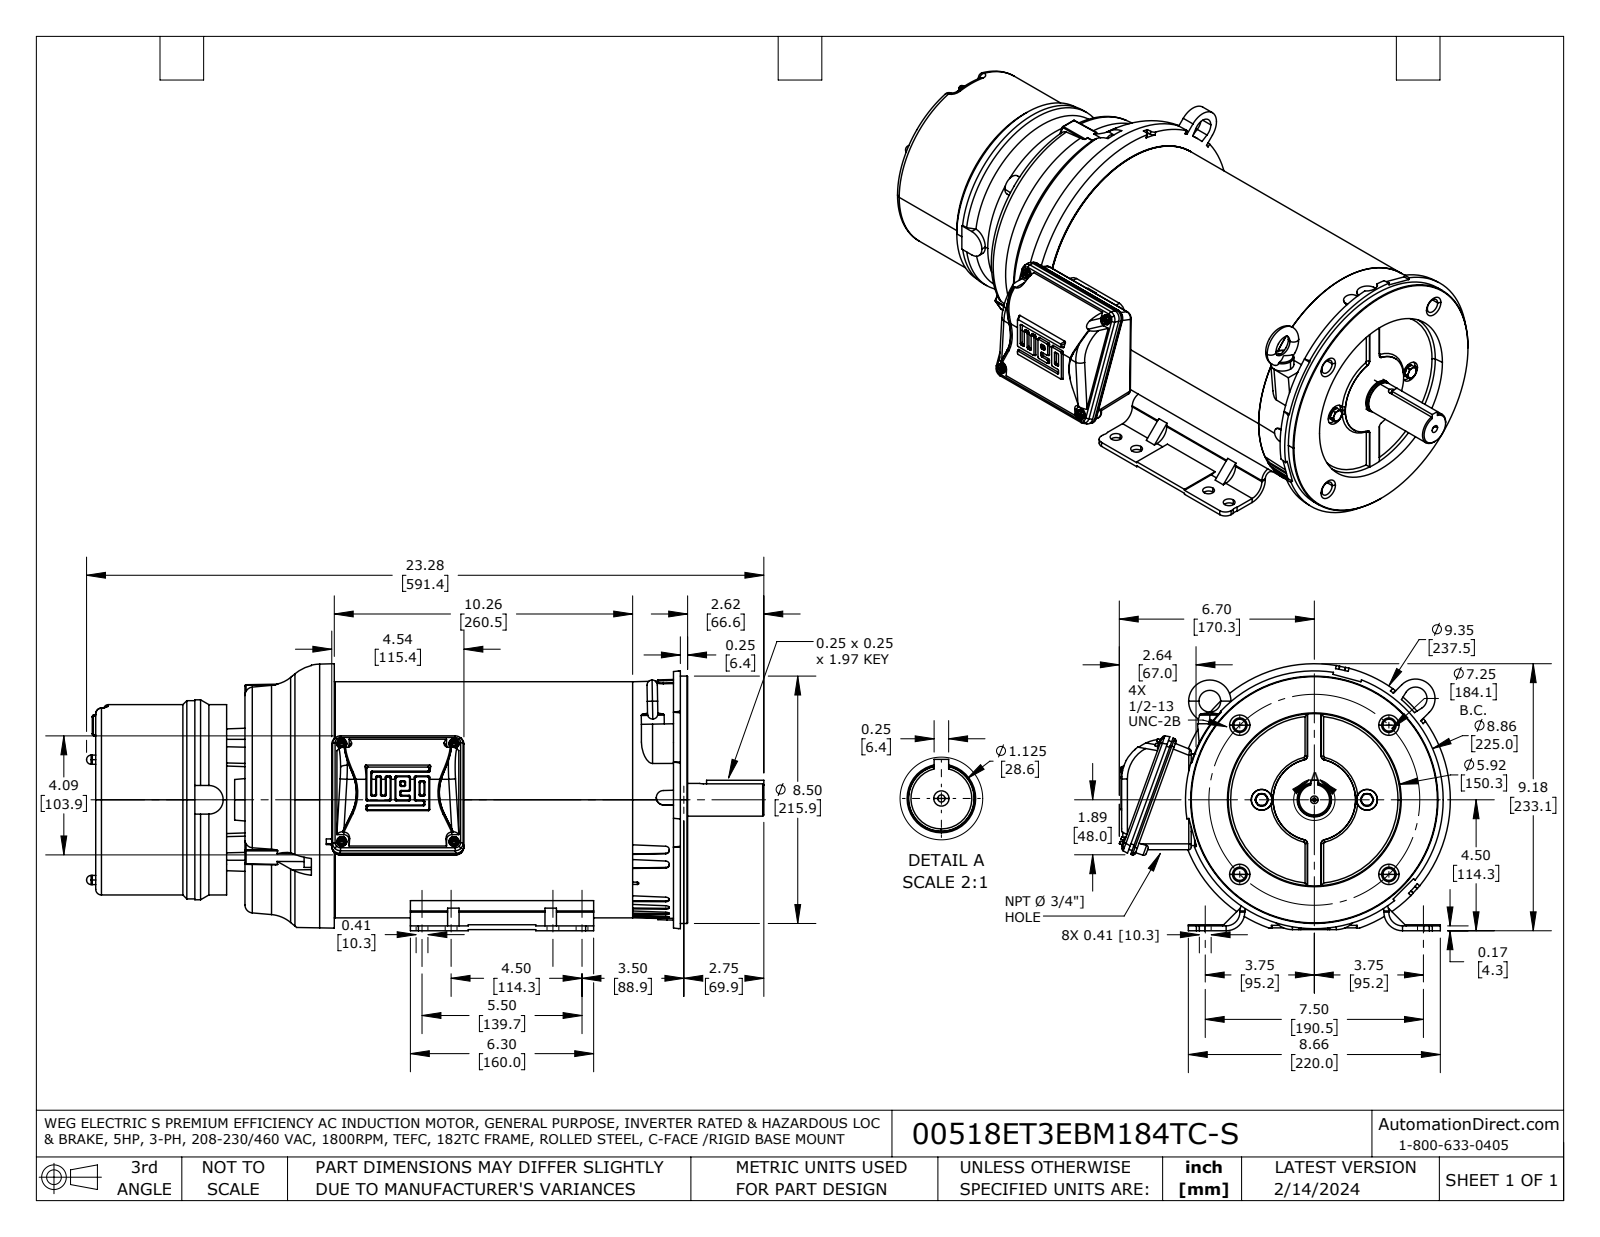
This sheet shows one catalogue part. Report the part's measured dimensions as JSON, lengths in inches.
{"part_name": "00518ET3EBM184TC-S", "step_written_by": "SolidWorks 2021 (AUTOMOTIVE_DESIGN)", "units": "inches", "bodies": {"solids": 21, "faces": 1366, "planar": 549, "cylindrical": 372, "other": 445}, "overall_size": [23.281, 11.38, 9.175], "volume_in3": 1003, "surface_area_in2": 1233, "round_holes": [[0.406, 8], [0.413, 4], [0.5, 4], [0.252, 2], [0.124, 1]], "round_bosses_or_shafts": [[0.348, 4], [0.375, 3], [0.315, 3], [0.25, 3], [0.433, 2], [0.35, 2], [8.5, 1], [8.114, 1]], "partial_cylinders_radius": [[0.047, 40], [0.126, 22], [0.039, 14], [0.087, 12], [0.276, 12], [0.079, 10], [0.118, 8], [0.205, 8]], "face_to_face_distances": [10.236, 3.72, 13.957, 0.167, 4.5, 8.22, 18.457, 20.346, 15.846, 12.126], "hole_center_spacings": [1, 4.5, 5.07, 7.5, 7.567, 8.746, 1.811, 2.671]}
